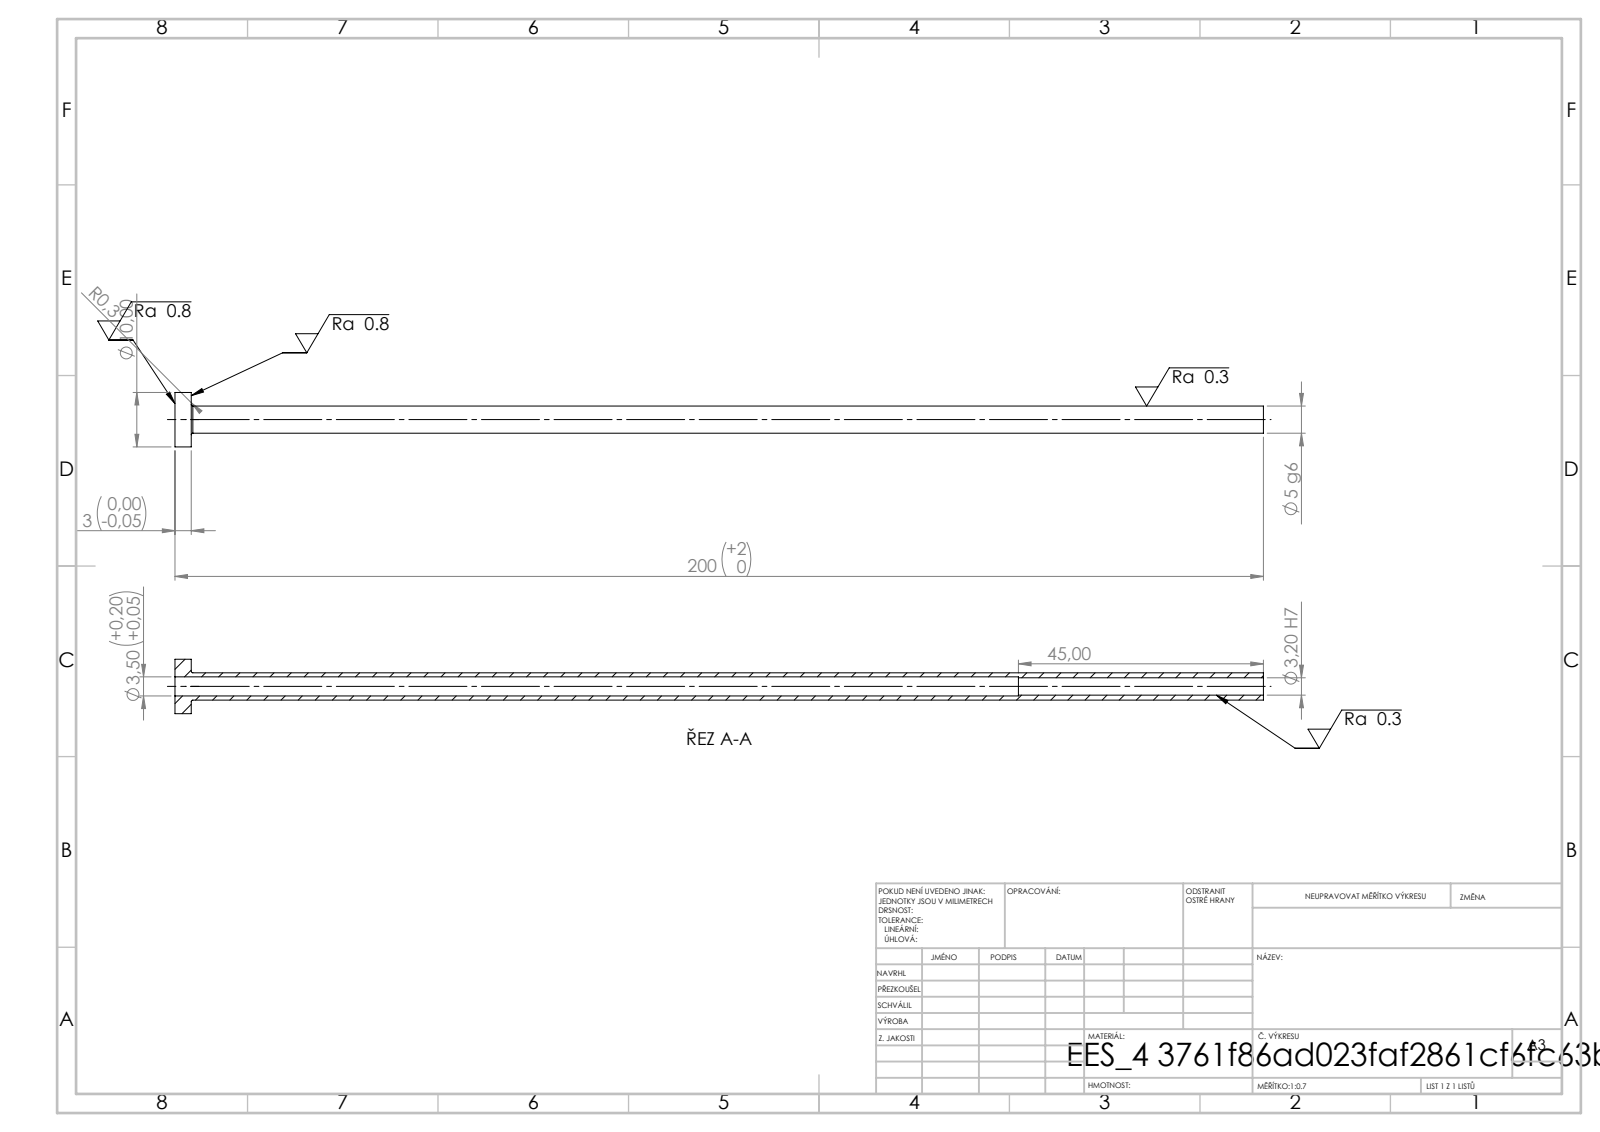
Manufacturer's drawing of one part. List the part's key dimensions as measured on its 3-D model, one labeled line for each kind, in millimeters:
STEP written by: SolidWorks 2019 (CONFIG_CONTROL_DESIGN)
Units: millimetres
Bodies: 1 solid, 14 faces (4 planar, 8 cylindrical, 2 other)
Overall size (bounding box): 200 × 10 × 10
Volume: 2 251 mm³ · Surface area: 5 484 mm²
Round holes (diameter × count): ⌀3.2 ×1, ⌀3.5 ×1
Round bosses / shafts (diameter × count): ⌀10 ×1, ⌀5 ×1
Main face-to-face distances: 3, 200, 197, 155, 152, 45
